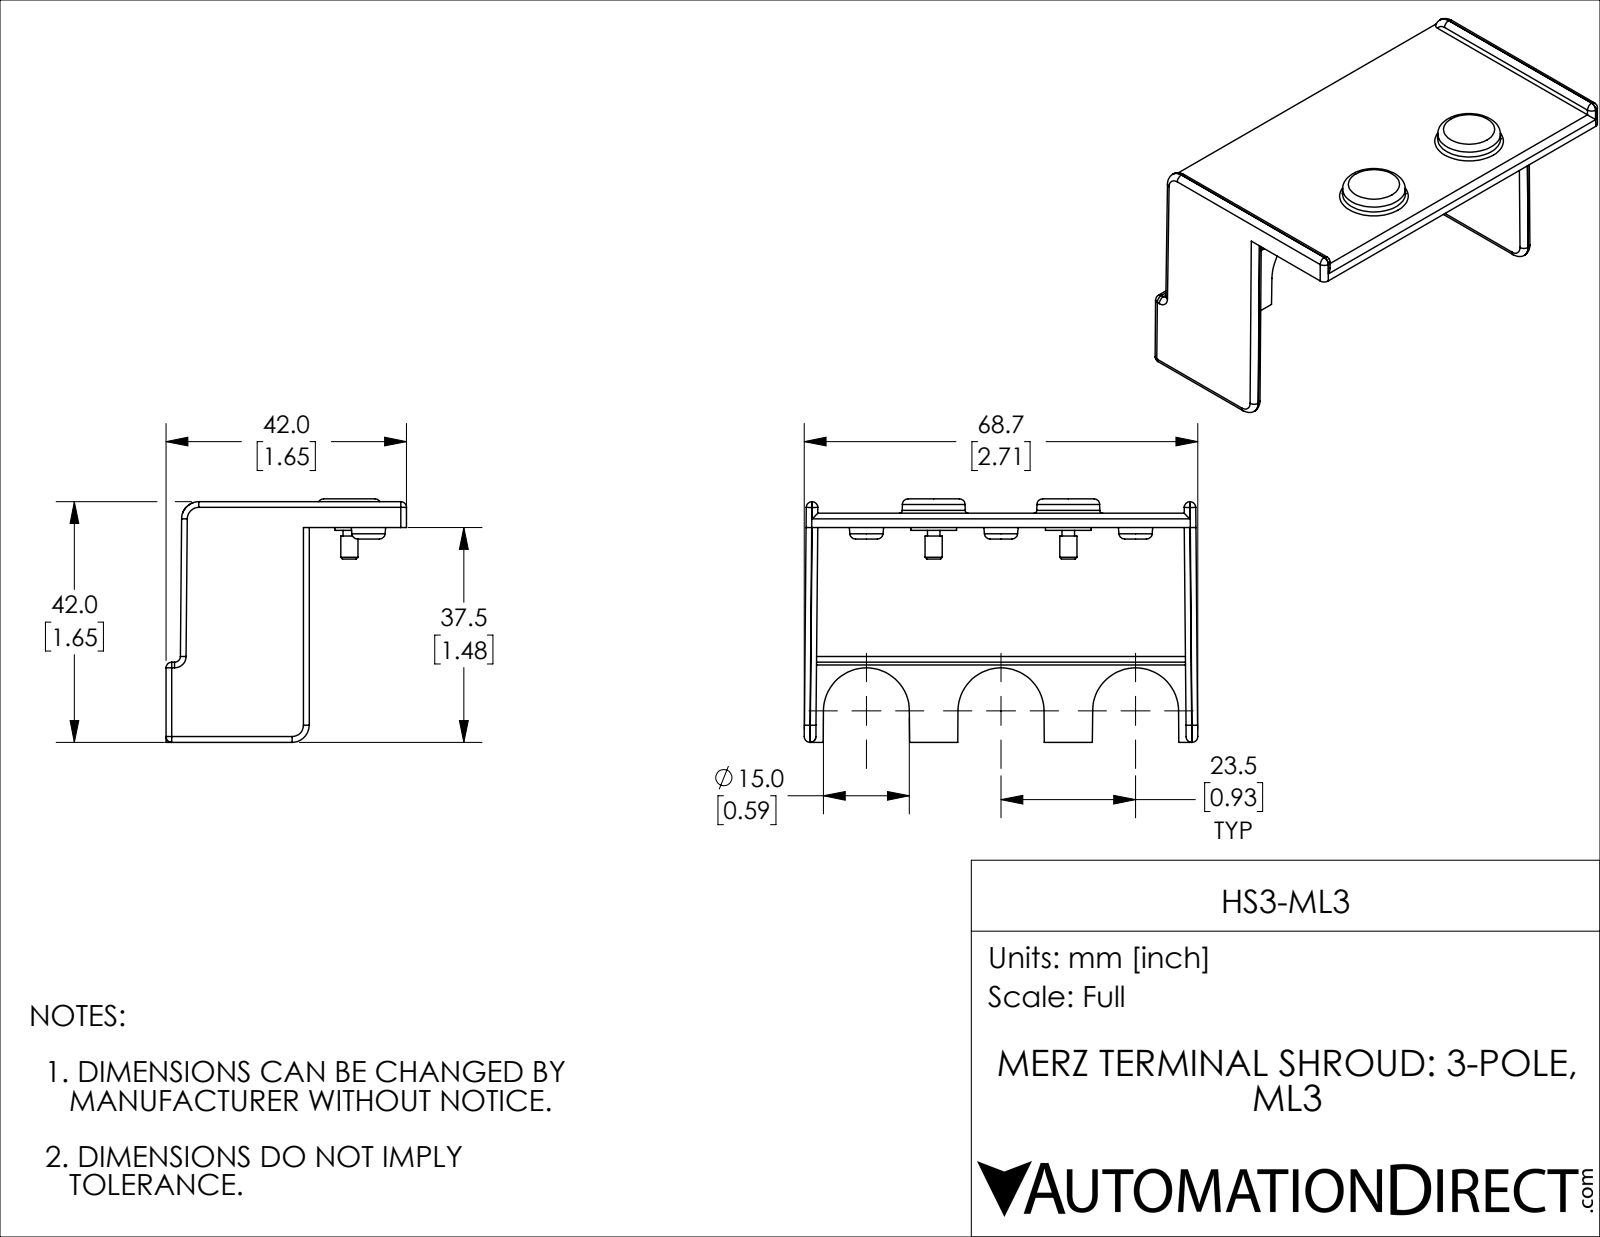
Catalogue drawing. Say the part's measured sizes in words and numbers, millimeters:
The part is named "HS3-ML3". Its 3-D file was written by "SolidWorks 2019 (AUTOMOTIVE_DESIGN)". It is 1 solid with 140 faces: 45 planar, 45 cylindrical and 50 other. Overall it measures 68.7 by 42.5 by 42 millimeters. Its volume is 14 900 cubic millimeters and its surface area 14 110 square millimeters. Round bosses or shafts: 2 of diameter 3, 2 of diameter 2.2. Partial cylindrical surfaces (rounded edges, fillets, slot ends): 28 of radius 1, 3 of radius 7.5, 2 of radius 3, 1 of radius 0.5. The main face-to-face distances are 2.5, 2, 1.8, 1.7, 5, 23.5, 42, 5.5, 0.5, 3.
